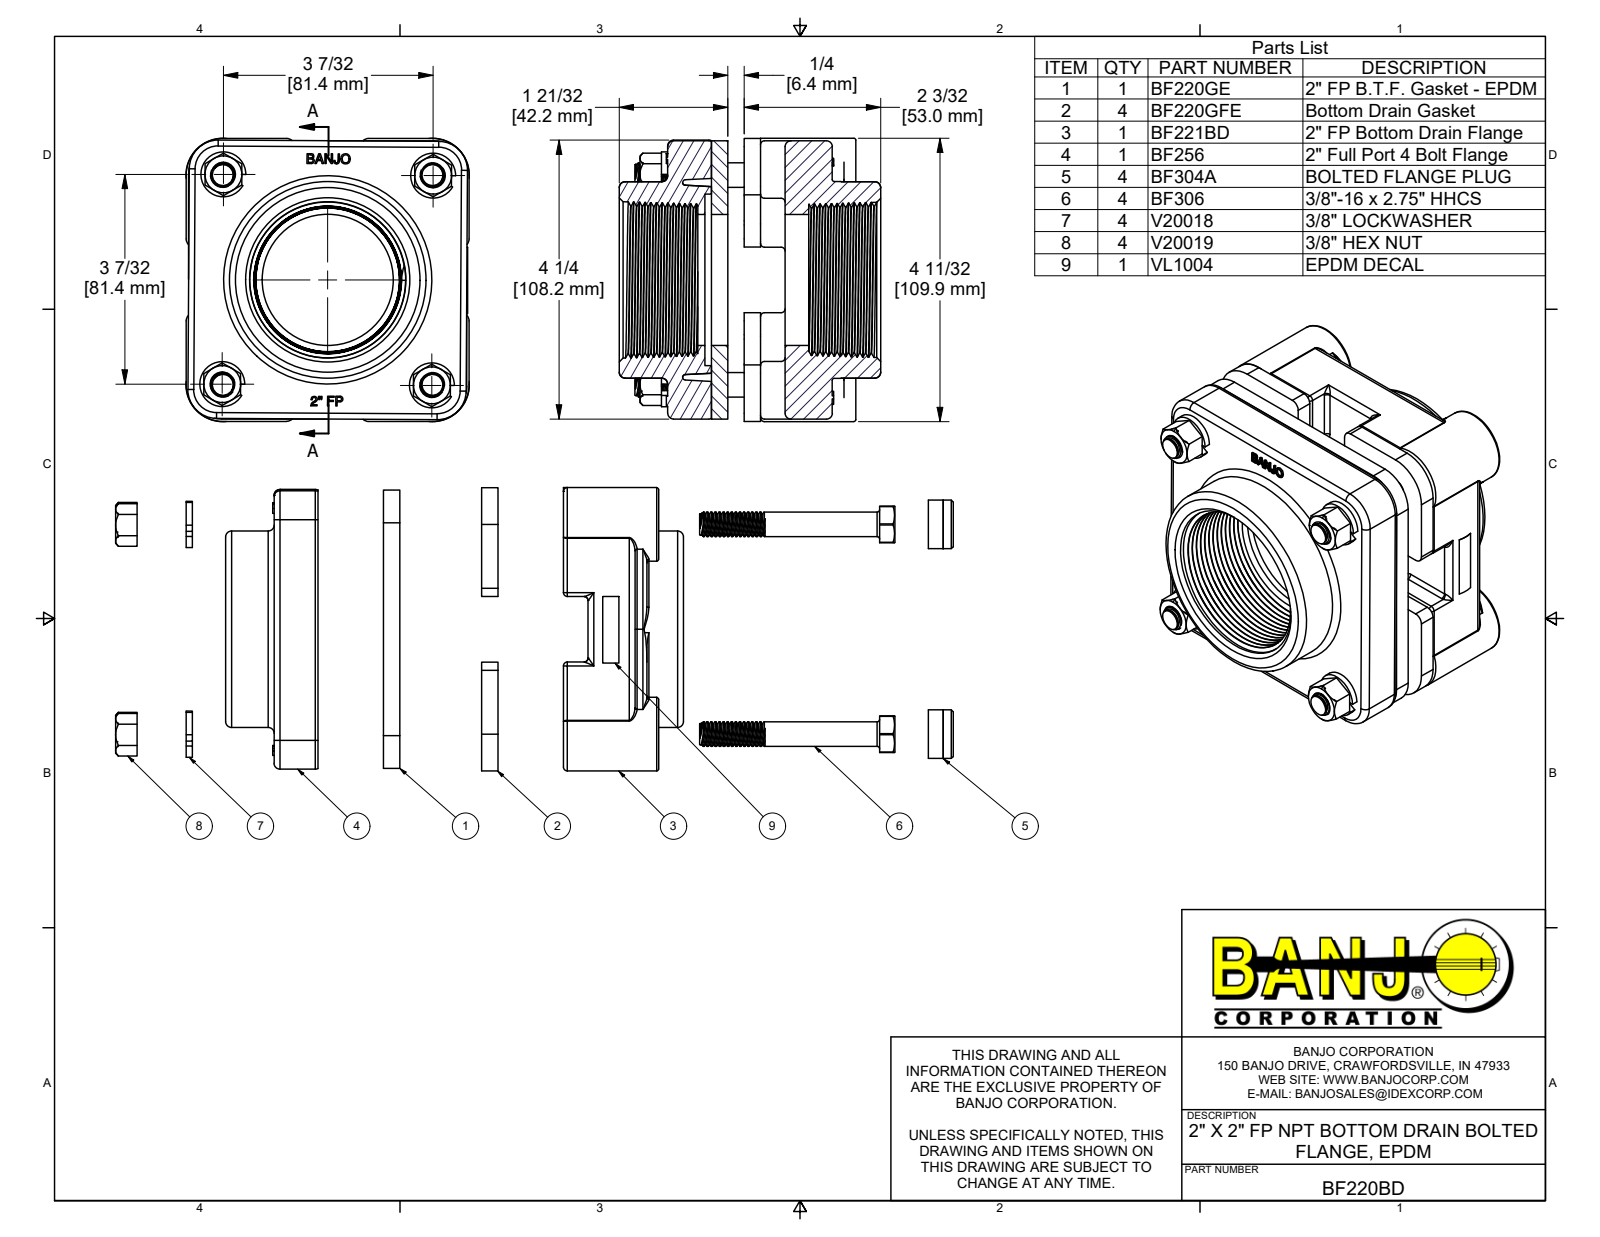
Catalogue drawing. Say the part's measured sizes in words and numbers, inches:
The part is named "BF220BD; BF221BD; BF220GFE; BF220GE (+7 more)". Its 3-D file was written by "Autodesk Inventor 2019 (AUTOMOTIVE_DESIGN)". It is 24 solids with 1428 faces: 422 planar, 433 cylindrical and 573 other. Overall it measures 38.212 by 4.328 by 4.328 inches. Its volume is 34.73 cubic inches and its surface area 524.8 square inches. Round holes: 4 of diameter 0.307, 4 of diameter 0.375, 4 of diameter 0.38, 4 of diameter 0.385, 4 of diameter 0.41, 4 of diameter 0.438, 4 of diameter 0.72, 4 of diameter 0.745, 1 of diameter 2, 1 of diameter 2.62, 1 of diameter 3. Round bosses or shafts: 60 of diameter 0.324, 4 of diameter 1.125, 4 of diameter 0.742, 4 of diameter 0.687, 4 of diameter 0.375. Partial cylindrical surfaces (rounded edges, fillets, slot ends): 44 of radius 0.06, 24 of radius 0.125, 16 of radius 0.09, 8 of radius 0.03, 8 of radius 0.162, 8 of radius 2, 4 of radius 0.32, 4 of radius 0.44. The main face-to-face distances are 0.25, 0.25, 4.25, 0.67, 0.92, 1.17, 0.5, 1.42, 0.75, 0.5. The hole center spacings are 0.013, 2.265, 2.266, 3.194, 3.203, 3.204, 3.213, 4.531.
